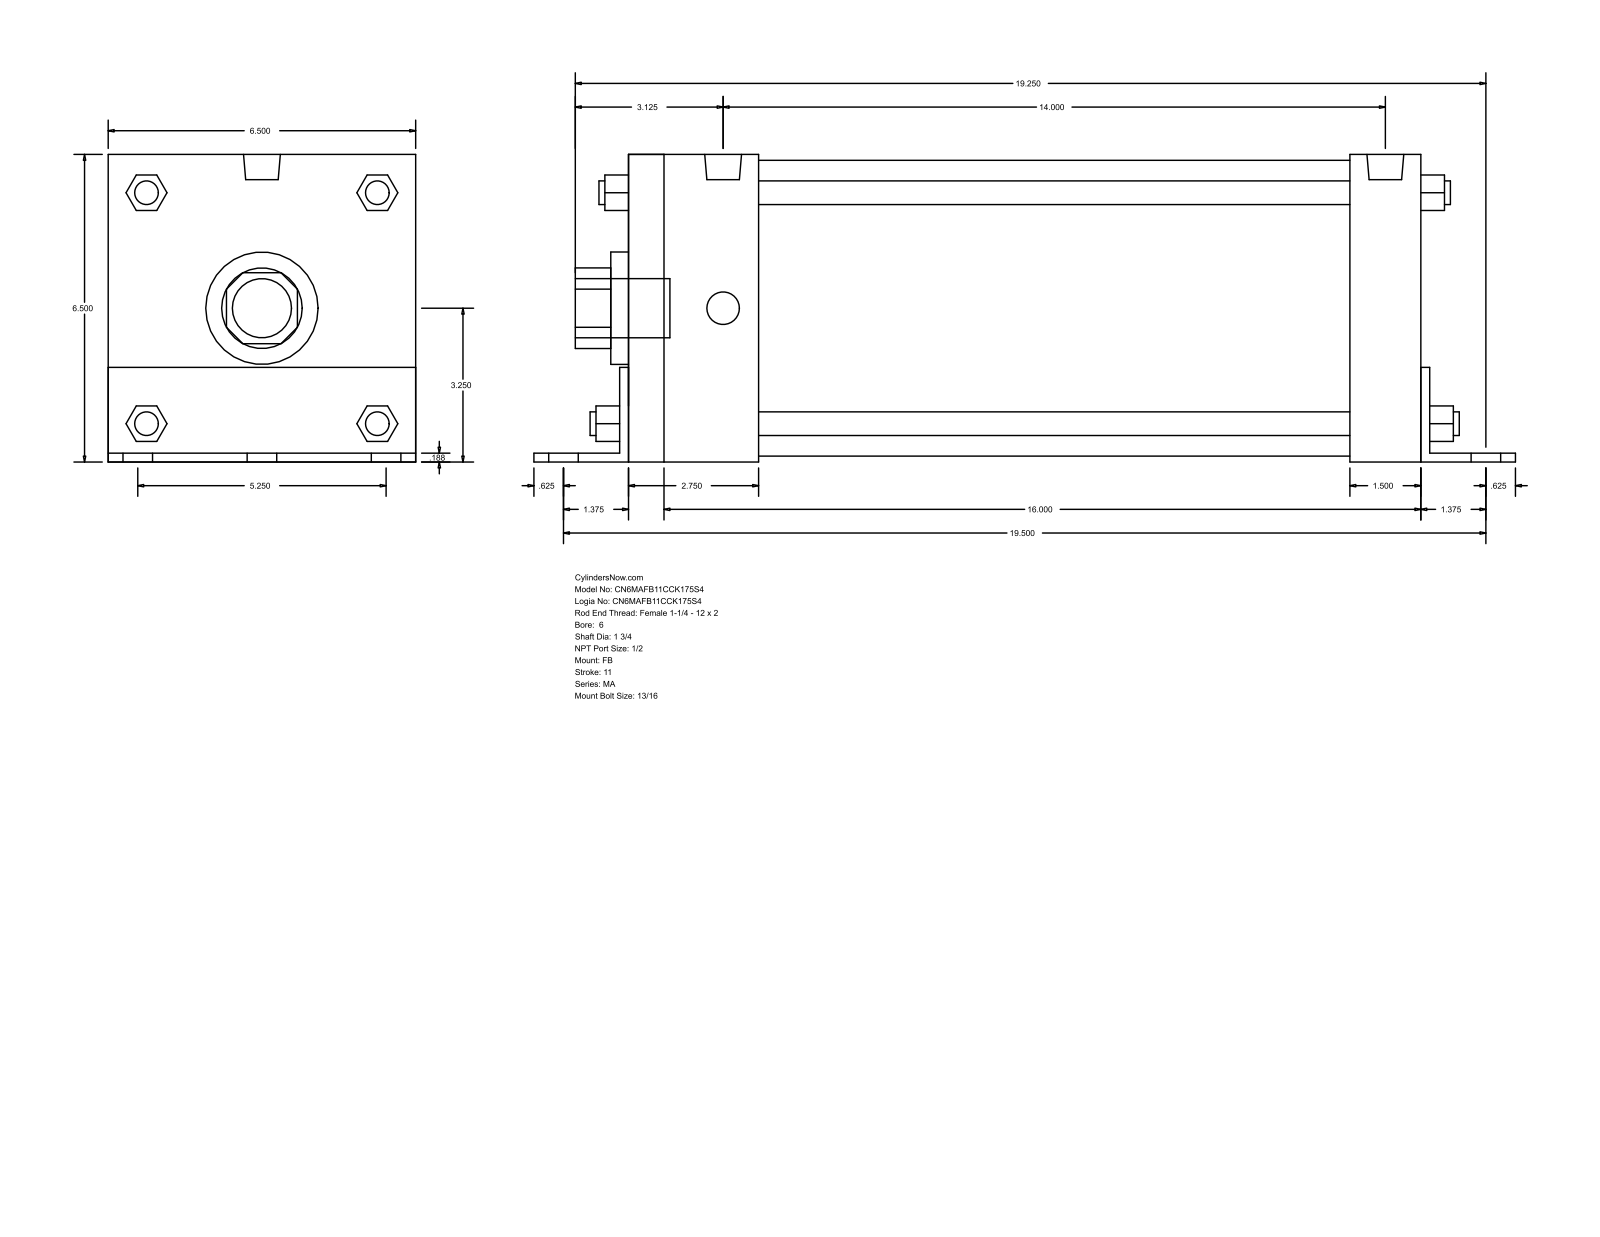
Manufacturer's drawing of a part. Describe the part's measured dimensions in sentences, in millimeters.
The part is named "MA_FB__0600_1.75". Its 3-D file was written by "GSSL Pune (CONFIG_CONTROL_DESIGN)". It is 0 solids with 140 faces: 105 planar, 35 cylindrical and 0 other. Overall it measures 527.05 by 165.15 by 165.1 millimeters. Round holes: 1 of diameter 44.45, 1 of diameter 60.33, 1 of diameter 158.75. Round bosses or shafts: 6 of diameter 20.64, 4 of diameter 17.46, 4 of diameter 12.7, 2 of diameter 19.77, 1 of diameter 31.75. Partial cylindrical surfaces (rounded edges, fillets, slot ends): 1 of radius 21.63, 1 of radius 32.05. The main face-to-face distances are 165.1, 4.76, 425.45, 165.15, 4.71, 160.39, 4.77, 38.09, 42.86, 430.22.
